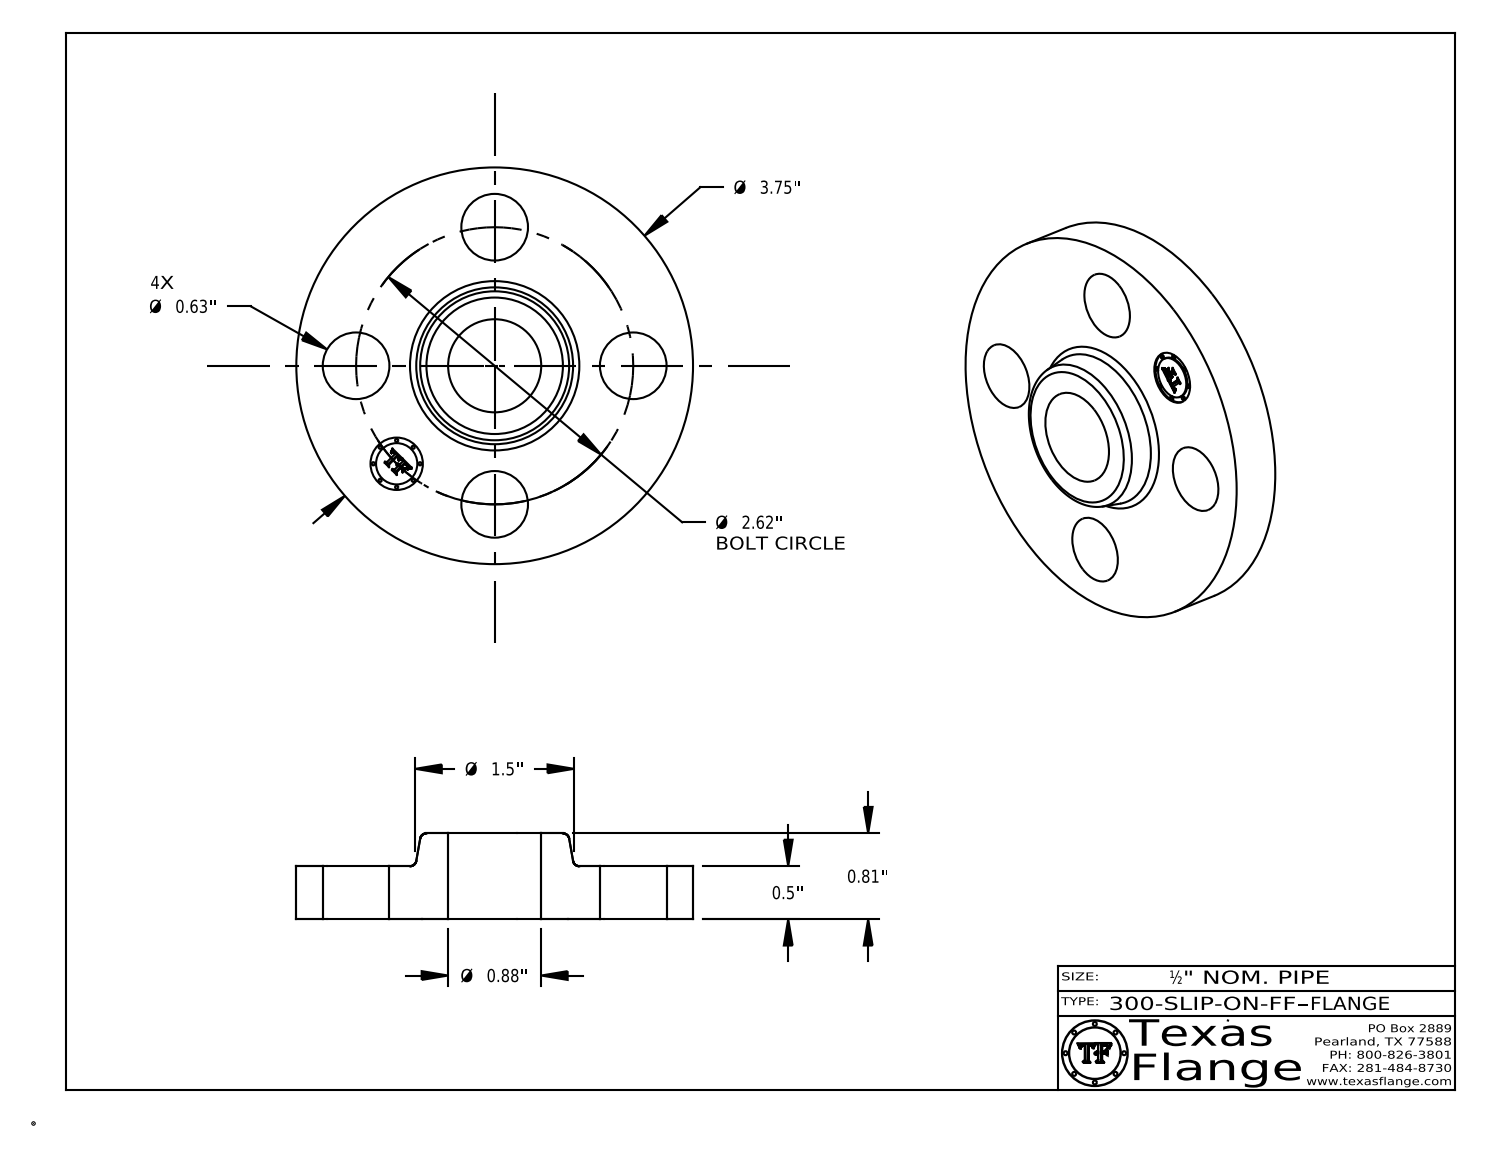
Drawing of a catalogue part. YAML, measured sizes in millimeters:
part_name: "300-SLIP-ON-FF"
step_written_by: "CATIA V5 STEP AP214 (AUTOMOTIVE_DESIGN)"
units: millimeters
bodies: {solids: 1, faces: 407, planar: 369, cylindrical: 32, other: 6}
overall_size: [95.3, 95.3, 20.6]
volume: 80530
surface_area: 20380
round_holes:
  - {diameter: 16, count: 4}
  - {diameter: 12.6, count: 1}
  - {diameter: 22.4, count: 1}
round_bosses_or_shafts:
  - {diameter: 0.8, count: 8}
  - {diameter: 95.3, count: 1}
  - {diameter: 9.9, count: 1}
face_to_face_distances: [12.7, 20.6, 7.9, 12.3, 0.4, 8.3, 3.8, 3.7, 0.7, 2.4]
hole_center_spacings: [33.3, 47, 25.5, 61.5, 66.5, 33.3]
